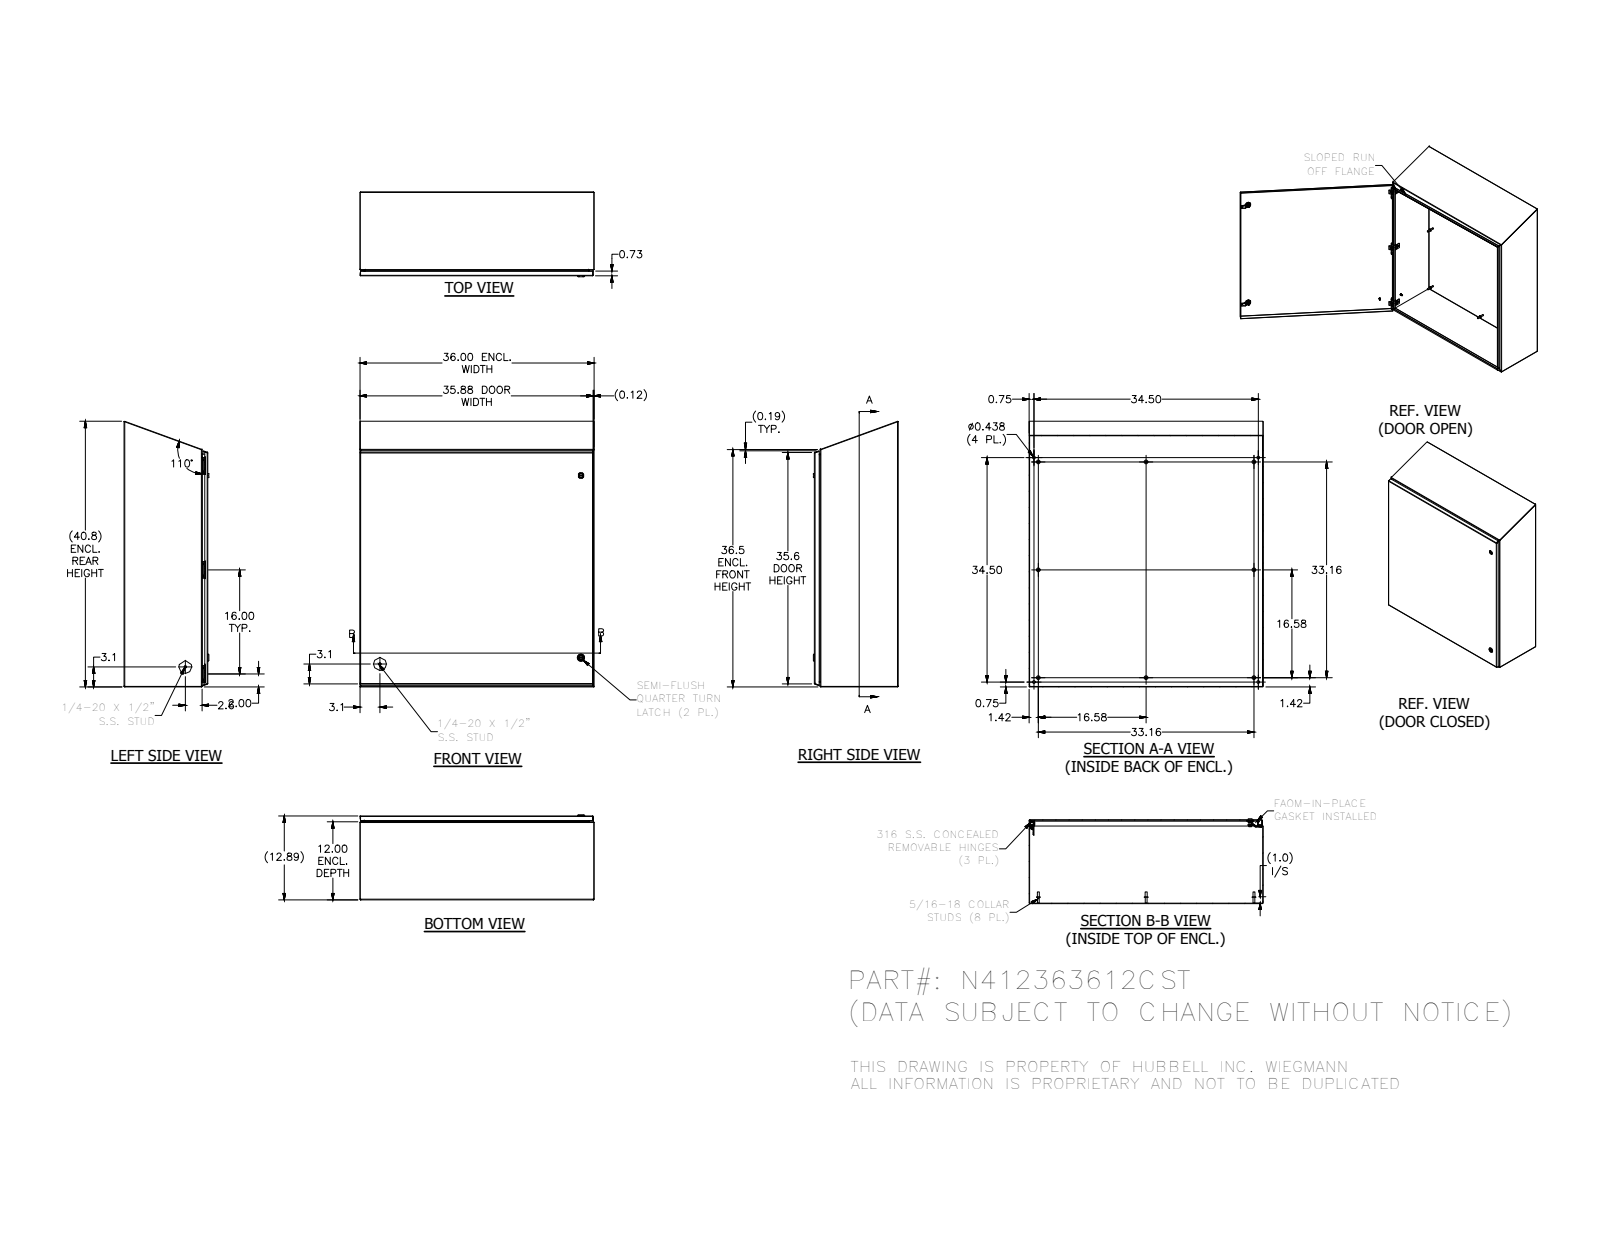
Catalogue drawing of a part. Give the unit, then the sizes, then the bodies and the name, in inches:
Units: inches
Overall size (bounding box): 40.847 × 36 × 13.044
Round holes (diameter × count): ⌀0.093 ×6, ⌀0.152 ×6, ⌀0.167 ×6, ⌀0.172 ×6, ⌀0.187 ×6, ⌀0.156 ×4, ⌀0.437 ×4, ⌀0.197 ×2, ⌀0.315 ×2, ⌀0.394 ×2, ⌀0.402 ×2, ⌀0.634 ×2
Round bosses / shafts (diameter × count): ⌀0.25 ×14, ⌀0.563 ×8, ⌀0.3 ×8, ⌀0.275 ×8, ⌀0.36 ×6, ⌀0.32 ×6, ⌀0.256 ×6, ⌀0.164 ×6
Partial cylindrical surfaces — rounded edges, fillets, slot ends (radius × count): R0.012 ×54, R0.05 ×38, R0.031 ×33, R0.016 ×26, R0.125 ×24, R0.02 ×23, R0.105 ×19, R0.032 ×12
Main face-to-face distances: 0.074, 12.813, 12.739, 12.887, 35.926, 35.852, 36, 11.926, 0.887, 0.813
Hole centre spacings: 16, 32, 16.008, 34.5, 0.5, 0.656, 0.66, 1.307
Volume: 361.7 in³ · Surface area: 9 839 in²
Bodies: 53 solids, 2386 faces (908 planar, 878 cylindrical, 600 other)
Part name (STEP PRODUCT): N412363612CSTB3S; HFW3161; 17376 PIN; 17380 SCREW (+8 more)
STEP written by: Autodesk Inventor 2014 (AUTOMOTIVE_DESIGN)
